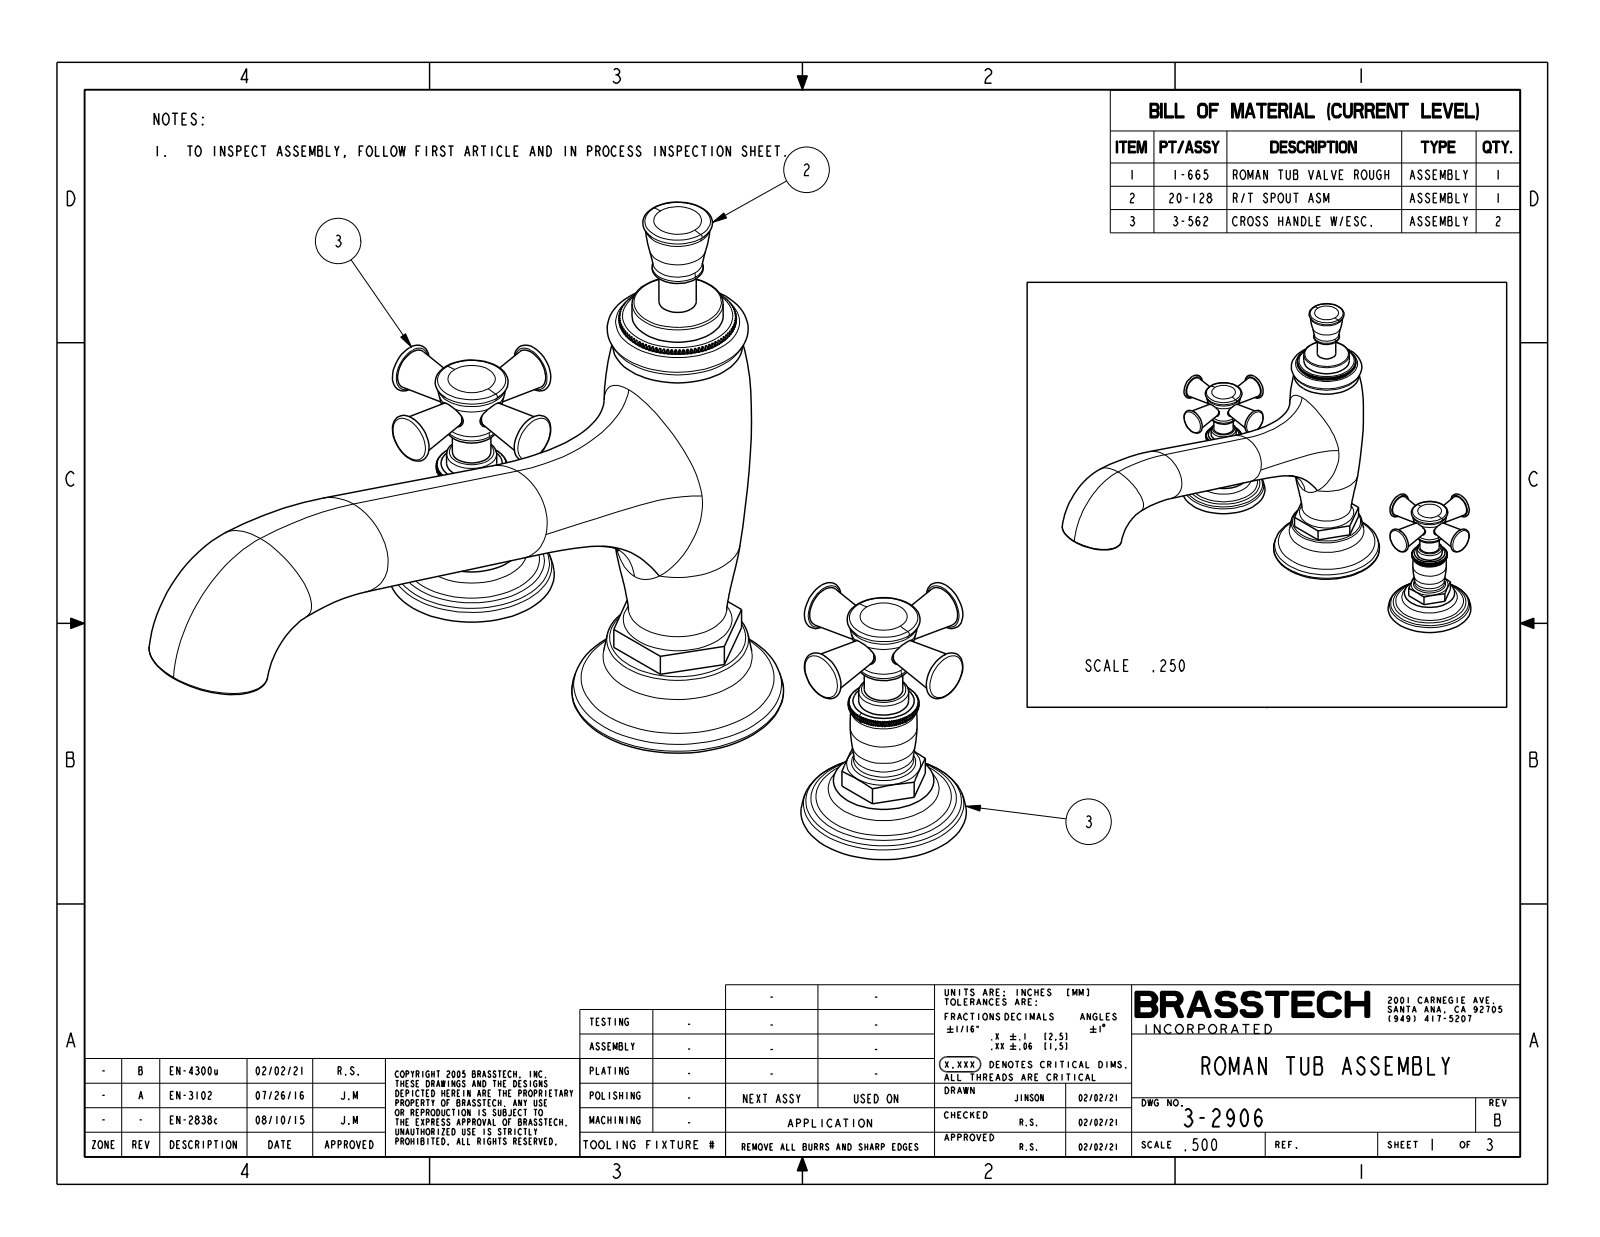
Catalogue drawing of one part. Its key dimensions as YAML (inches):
part_name: "3-2906"
step_written_by: "CREO PARAMETRIC BY PTC INC, 2018400 (CONFIG_CONTROL_DESIGN)"
units: inches
bodies: {solids: 3, faces: 1045, planar: 607, cylindrical: 18, other: 420}
overall_size: [11.244, 10.45, 7.987]
volume: 41.66
surface_area: 146.3
round_bosses_or_shafts:
  - {diameter: 0.98, count: 2}
  - {diameter: 0.686, count: 2}
  - {diameter: 0.53, count: 2}
  - {diameter: 1.25, count: 1}
  - {diameter: 0.51, count: 1}
  - {diameter: 0.35, count: 1}
face_to_face_distances: [0.534, 6.583, 6.05, 1.575, 2.164, 3.739, 3.189, 4.764, 1.025, 6.928]
